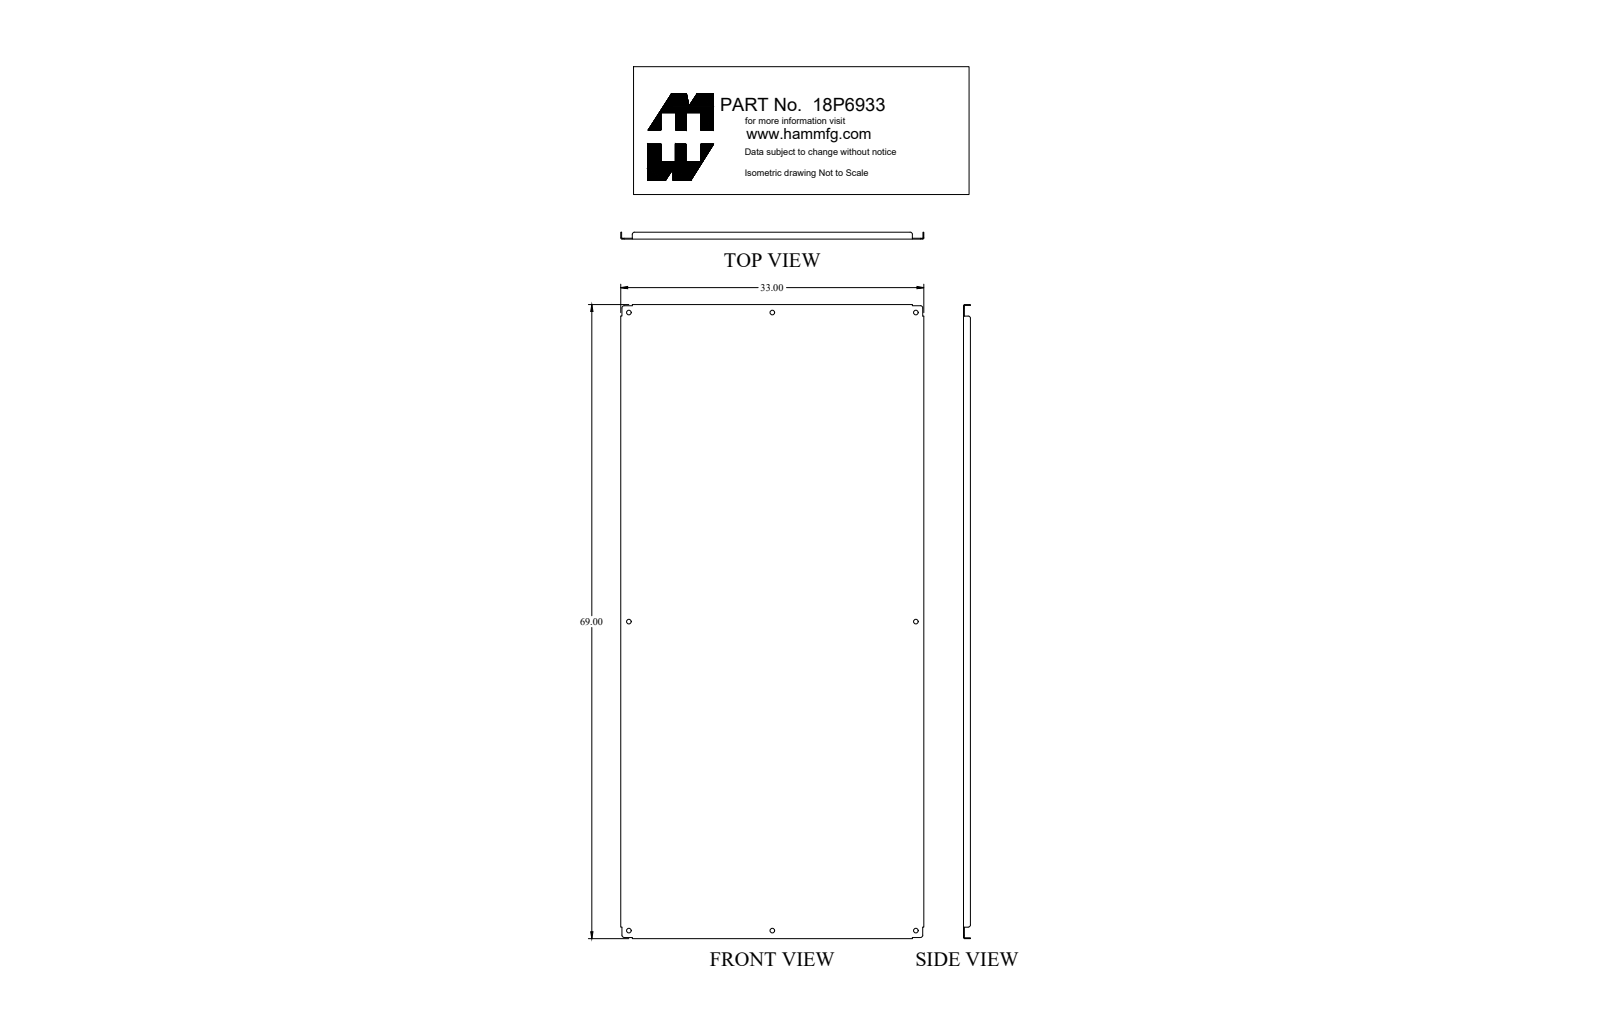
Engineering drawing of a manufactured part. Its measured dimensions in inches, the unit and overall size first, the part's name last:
Units: inches
Overall size (bounding box): 69 × 33 × 0.75
Round holes (diameter × count): ⌀0.5 ×8
Partial cylindrical surfaces — rounded edges, fillets, slot ends (radius × count): R0.25 ×8, R0.03 ×4, R0.125 ×4
Main face-to-face distances: 0.095, 32.905, 32.81, 33, 68.905, 69, 68.81, 0.75, 0.655, 1.252
Hole centre spacings: 15.625, 33.625, 37.078, 45.904, 69.041, 31.25, 67.25, 74.156
Volume: 227.5 in³ · Surface area: 4 810 in²
Bodies: 1 solid, 66 faces (30 planar, 36 cylindrical, 0 other)
Part name (STEP PRODUCT): 18P6933_Default
STEP written by: SolidWorks 2018 (CONFIG_CONTROL_DESIGN)
